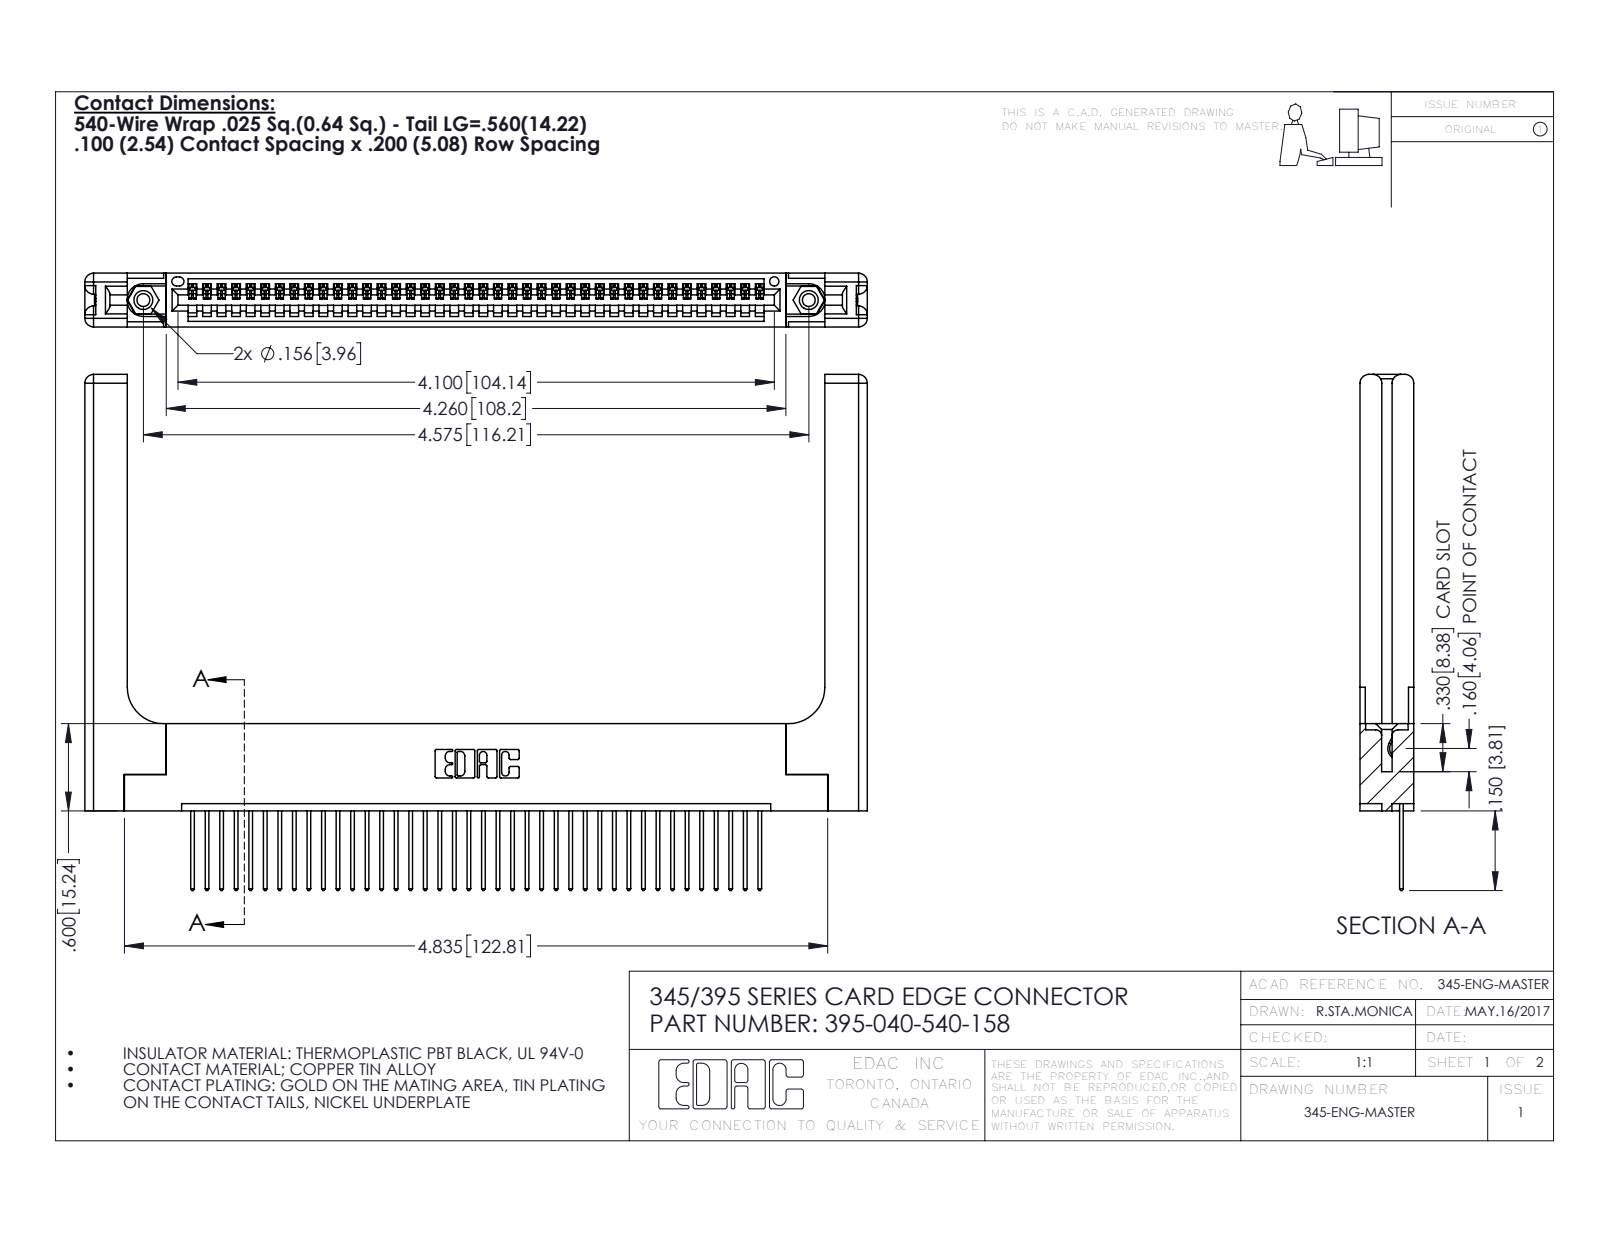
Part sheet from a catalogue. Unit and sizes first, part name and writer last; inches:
Units: inches
Overall size (bounding box): 5.379 × 3.547 × 0.37
Round holes (diameter × count): ⌀0.089 ×2, ⌀0.125 ×2, ⌀0.156 ×2, ⌀0.064 ×1
Round bosses / shafts (diameter × count): ⌀0.155 ×2
Partial cylindrical surfaces — rounded edges, fillets, slot ends (radius × count): R0.006 ×80, R0.01 ×80, R0.01 ×22, R0.06 ×16, R0.007 ×6, R0.031 ×6, R0.026 ×3, R0.03 ×2
Main face-to-face distances: 0.072, 0.37, 0.298, 0.2, 0.098, 0.272, 0.025, 0.148, 0.15, 0.225
Hole centre spacings: 0.27, 4.339, 4.575
Volume: 1.313 in³ · Surface area: 35.59 in²
Bodies: 45 solids, 2702 faces (1828 planar, 814 cylindrical, 60 other)
Part name (STEP PRODUCT): 345-220-058_345-220-058; 345 Part_Flush Mounting Lugs - 0.156 Dia-TH; 395-040-540-158; 345-250-001_345-250-001-102 (+1 more)
STEP written by: SolidWorks 2016 (CONFIG_CONTROL_DESIGN)
